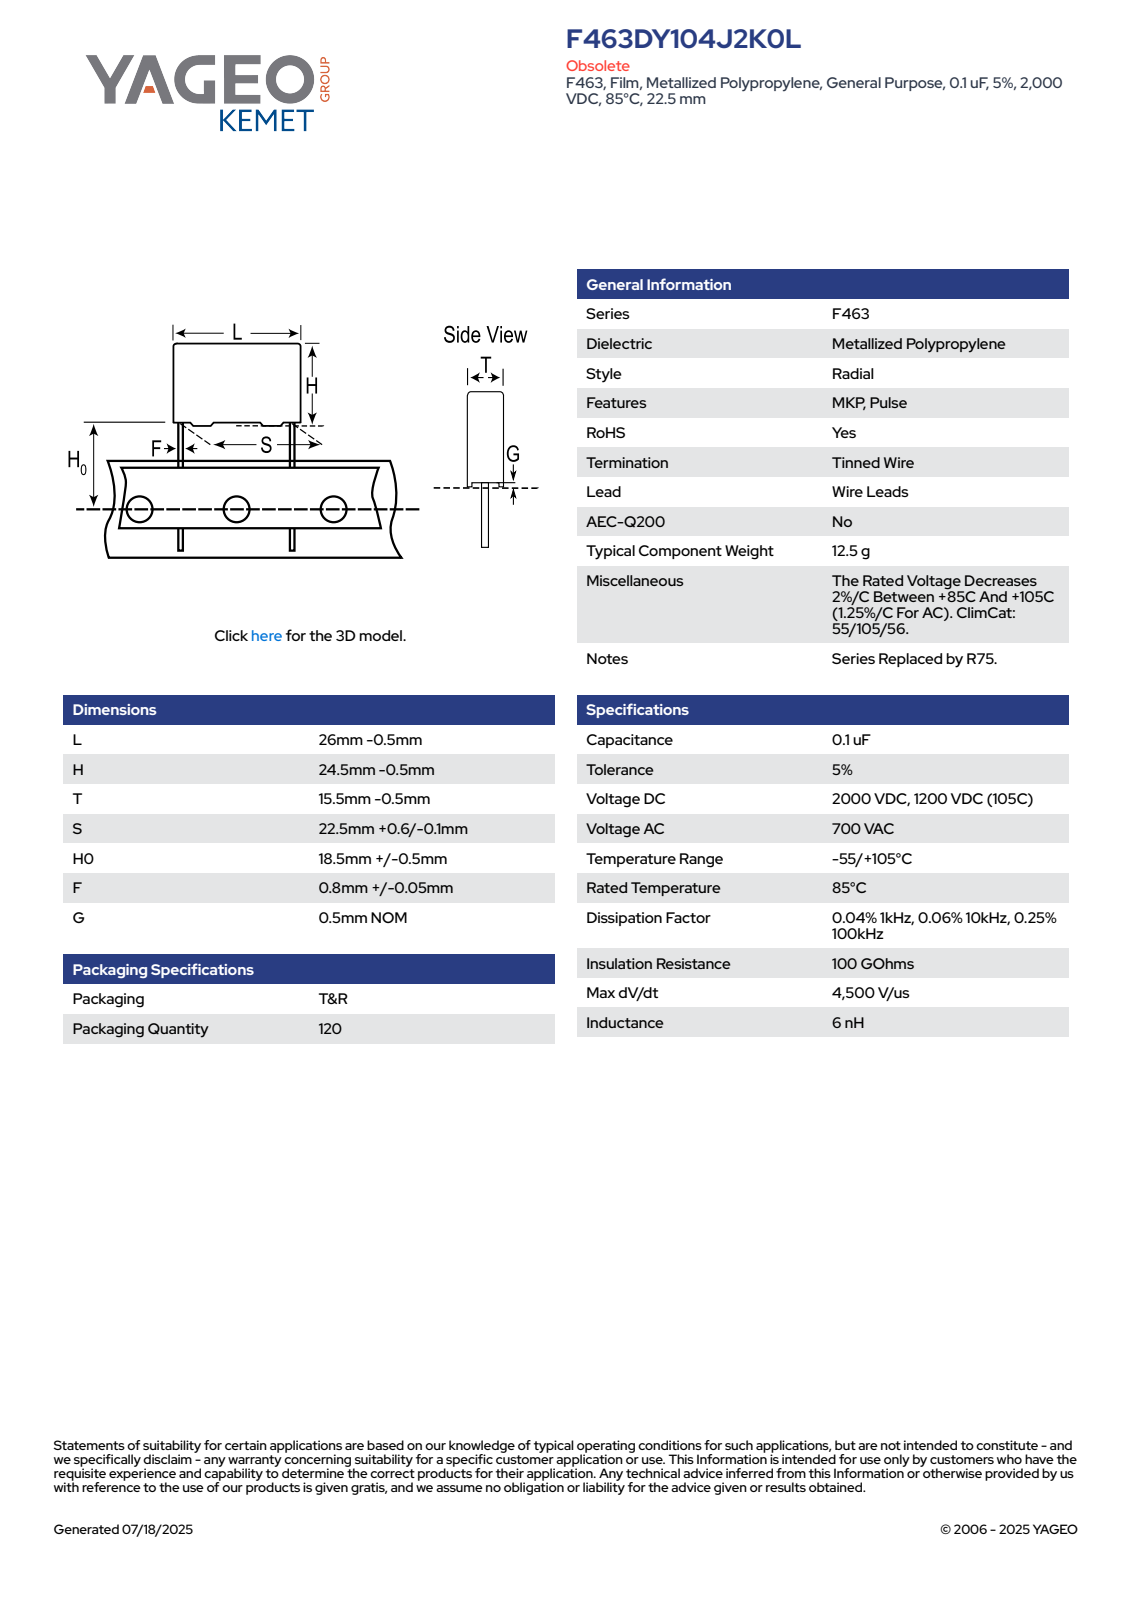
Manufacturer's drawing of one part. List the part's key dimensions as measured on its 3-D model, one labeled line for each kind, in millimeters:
Part name (STEP PRODUCT): CFR_RBG_26X24.5X15.5_L25.5H24T15S22.5H019F0.85G0.5
STEP written by: SolidWorks 2014 (AUTOMOTIVE_DESIGN)
Units: millimetres
Bodies: 4 solids, 89 faces (81 planar, 8 cylindrical, 0 other)
Overall size (bounding box): 43 × 25.5 × 15.01
Volume: 9 014 mm³ · Surface area: 2 844 mm²
Round bosses / shafts (diameter × count): ⌀0.85 ×2
Partial cylindrical surfaces — rounded edges, fillets, slot ends (radius × count): R0.5 ×4
Main face-to-face distances: 15, 25.5, 23.5, 0.5, 24, 0.85, 14.14, 0.86, 13.29, 14.15
